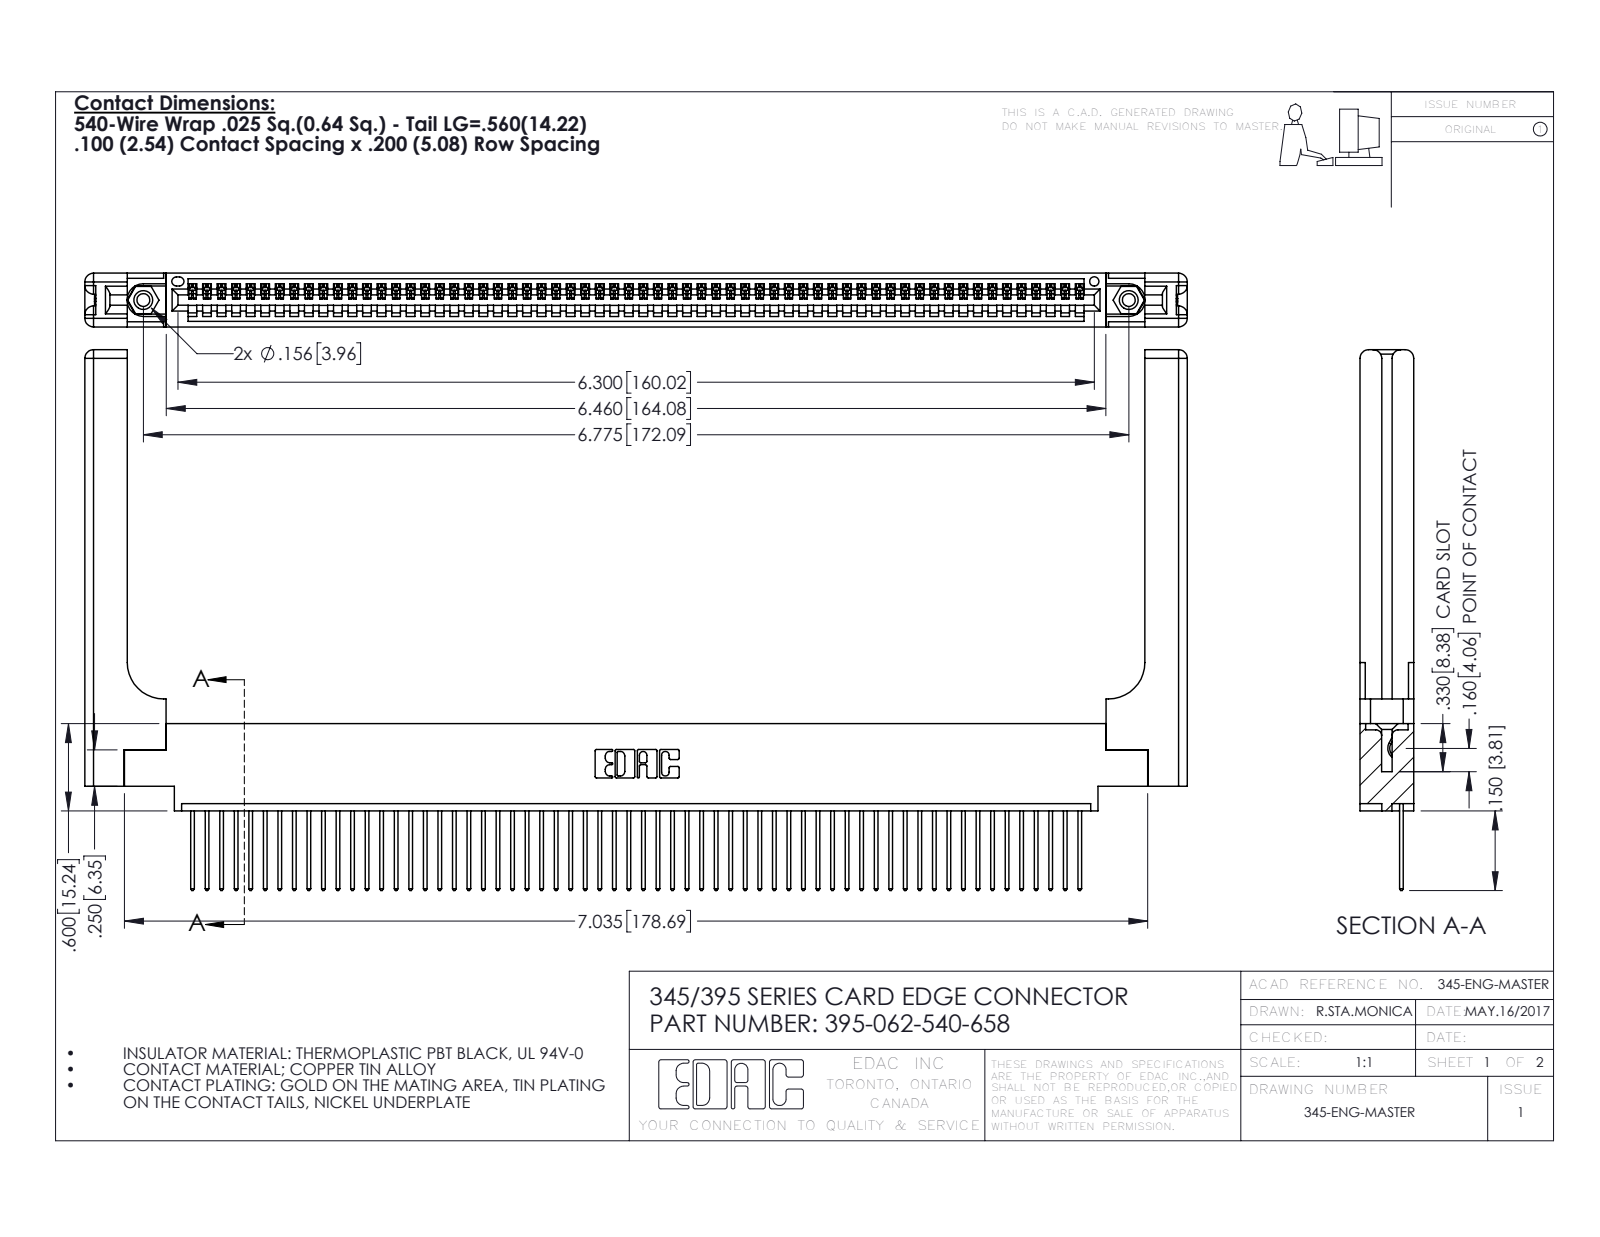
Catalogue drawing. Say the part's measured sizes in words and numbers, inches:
The part is named "345-220-058_345-220-058; 345-250-001_345-250-001-102; 345 Part_0.170 Offset - 0.156 Dia-TH; 345-292-001_345-293-140 (+1 more)". Its 3-D file was written by "SolidWorks 2016 (CONFIG_CONTROL_DESIGN)". It is 67 solids with 3982 faces: 2712 planar, 1210 cylindrical and 60 other. Overall it measures 7.579 by 3.717 by 0.37 inches. Its volume is 1.643 cubic inches and its surface area 47.72 square inches. Round holes: 2 of diameter 0.089, 2 of diameter 0.125, 2 of diameter 0.156, 1 of diameter 0.064. Round bosses or shafts: 2 of diameter 0.155. Partial cylindrical surfaces (rounded edges, fillets, slot ends): 124 of radius 0.006, 124 of radius 0.01, 22 of radius 0.01, 16 of radius 0.06, 6 of radius 0.007, 6 of radius 0.031, 3 of radius 0.026, 2 of radius 0.03. The main face-to-face distances are 0.072, 0.298, 0.37, 0.098, 0.272, 0.025, 0.2, 0.225, 0.15, 0.148. The hole center spacings are 0.27, 6.539, 6.775.
